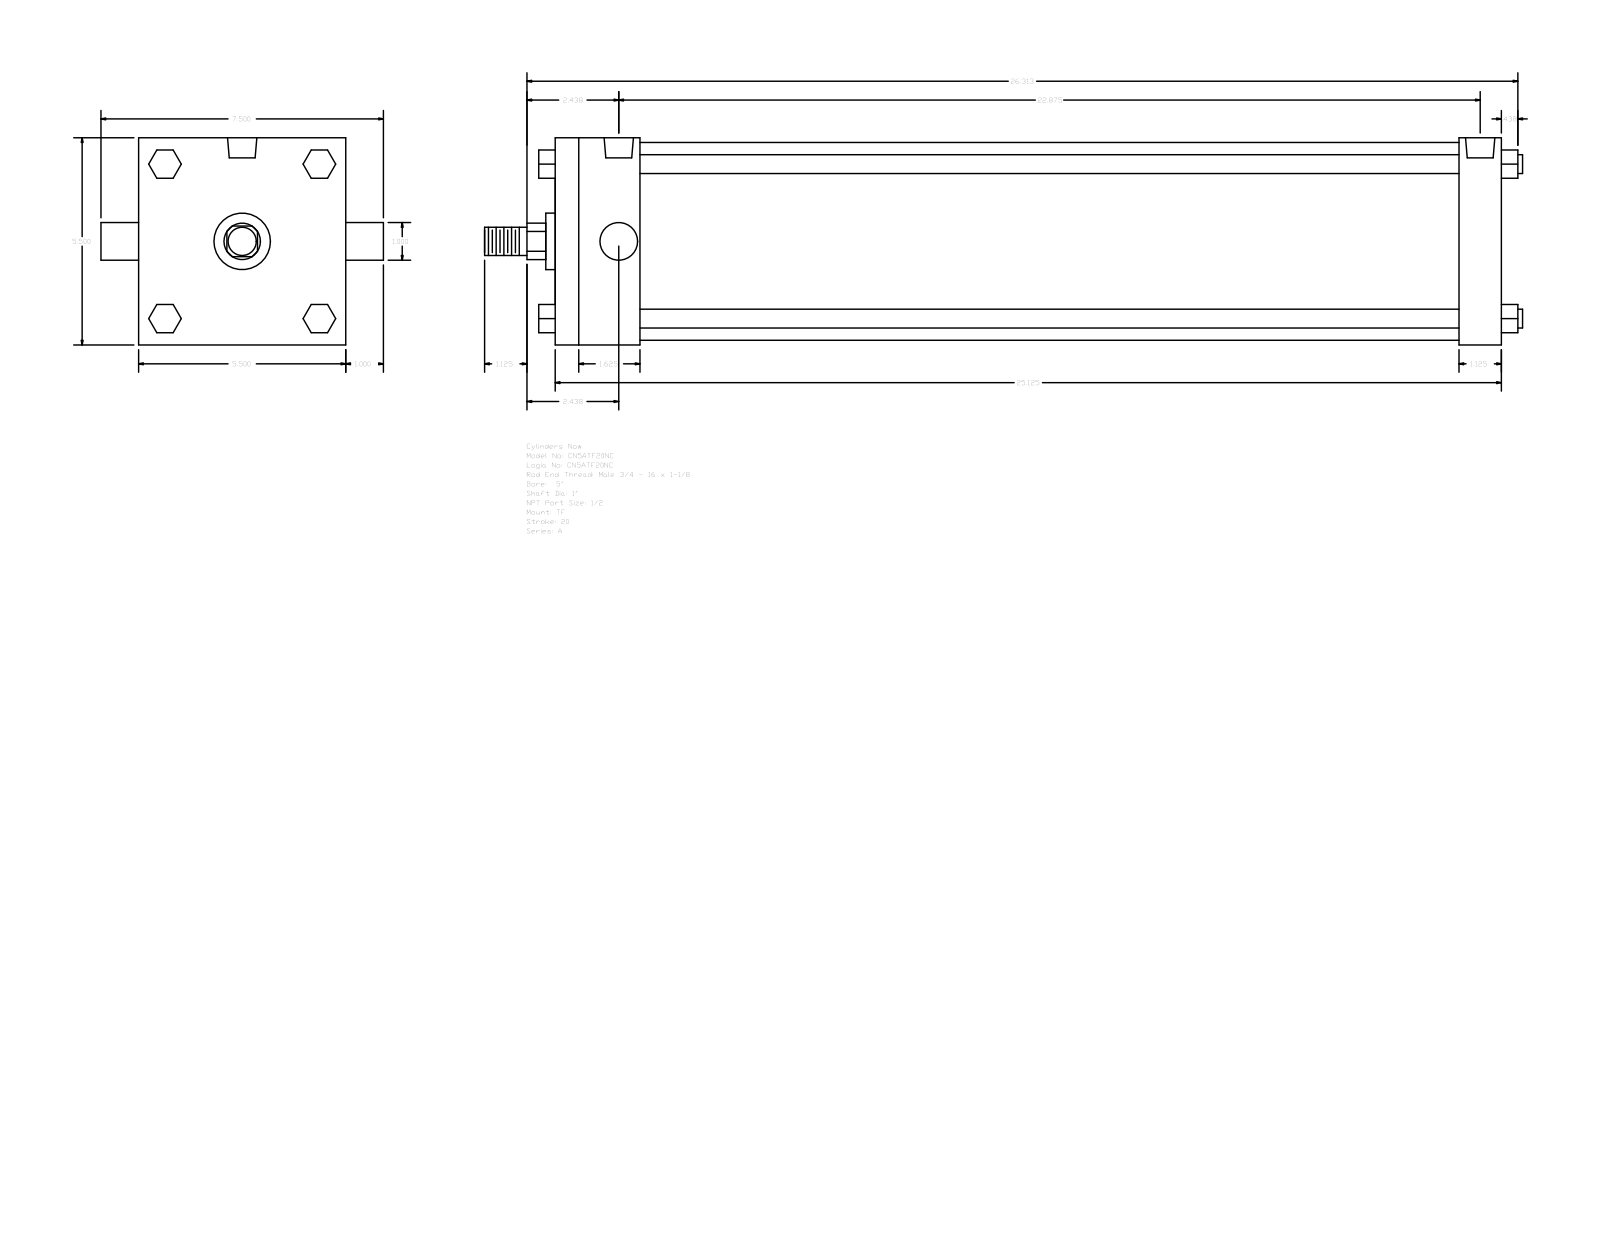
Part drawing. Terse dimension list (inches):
name: A_TF__0500_1
written by: GSSL Pune (CONFIG_CONTROL_DESIGN)
unit: in
bodies: 0 solids, 120 faces (92 planar, 28 cylindrical, 0 other)
size: 27.563 × 7.5 × 5.5
holes: 3× ⌀0.344, 2× ⌀0.778
bosses: 4× ⌀0.5, 2× ⌀1, 1× ⌀5.25, 1× ⌀1.5, 1× ⌀0.75
rounds: 1× R0.484
face distances: 5.5, 25.125, 24, 1.125, 2.25, 21.75, 22.875, 0.75, 2.05, 3.55
hole spacings: 0.094, 22.781, 22.687, 22.875
